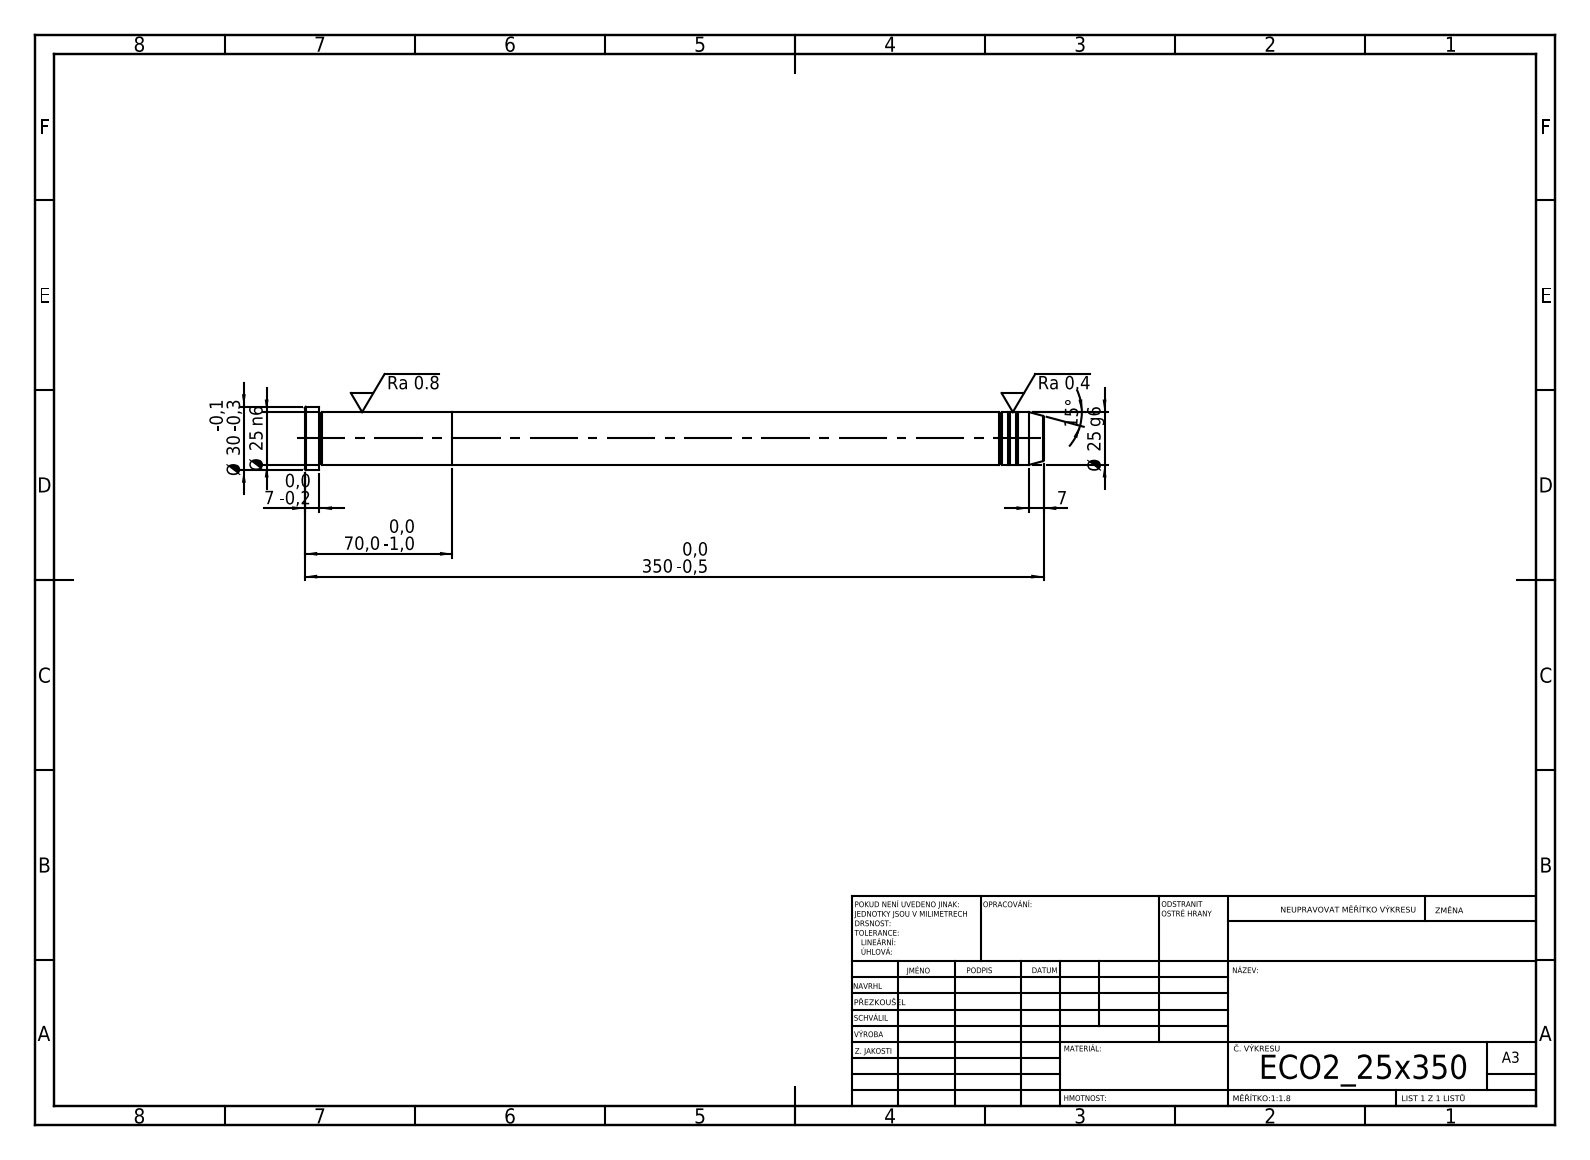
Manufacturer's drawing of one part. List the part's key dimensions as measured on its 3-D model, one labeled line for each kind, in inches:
STEP written by: SolidWorks 2019 (CONFIG_CONTROL_DESIGN)
Units: inches
Bodies: 2 solids, 39 faces (5 planar, 12 cylindrical, 22 other)
Overall size (bounding box): 13.78 × 1.181 × 1.181
Volume: 10.54 in³ · Surface area: 46.45 in²
Round bosses / shafts (diameter × count): ⌀1.181 ×1, ⌀0.984 ×1
Main face-to-face distances: 2.756, 11.024, 13.78, 13.504, 2.48, 0.276
